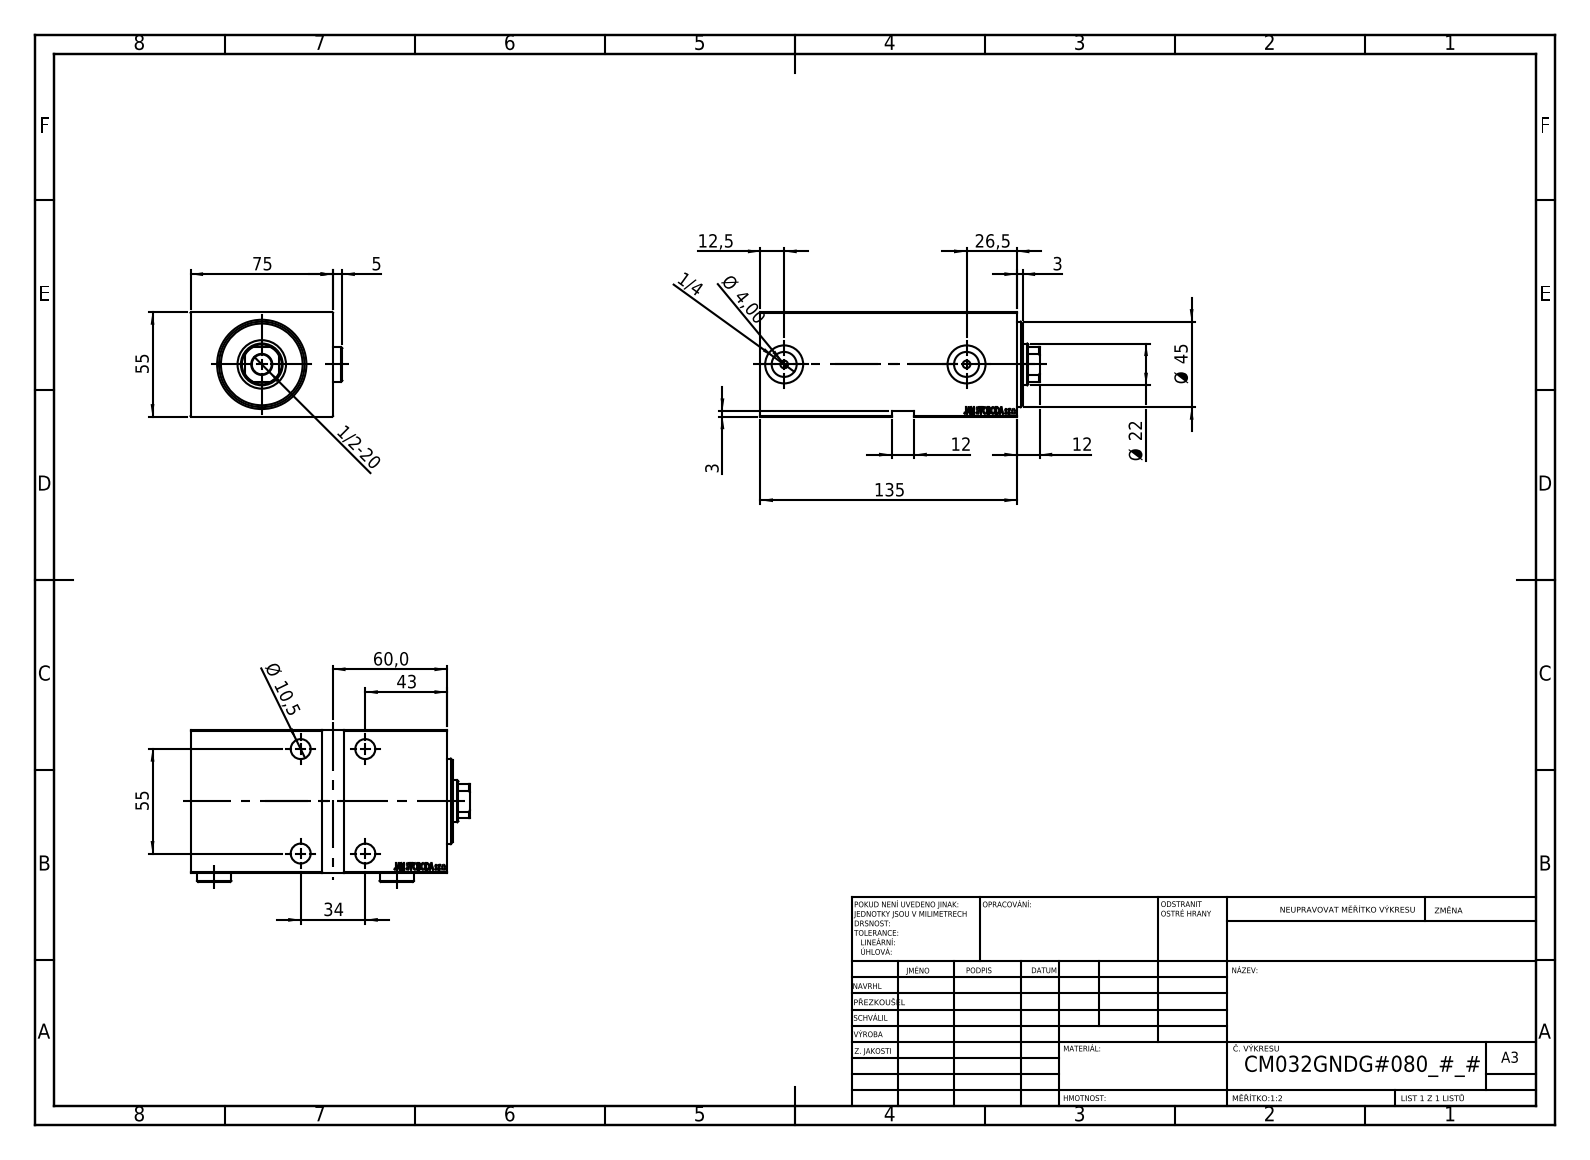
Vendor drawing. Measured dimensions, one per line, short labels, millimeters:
name: Zatka_OIL_PORT; V450CM_G_VCP; V450CM_VC_G; V450CM_G_Body
written by: SolidWorks 2019 (CONFIG_CONTROL_DESIGN)
unit: mm
bodies: 5 solids, 912 faces (446 planar, 68 cylindrical, 398 other)
size: 147 × 79.9 × 55
volume: 491 329 mm³; area: 86 215 mm²
holes: 5× ⌀10.5, 4× ⌀16.5, 2× ⌀4, 2× ⌀13.16, 2× ⌀20, 1× ⌀22, 1× ⌀25.5, 1× ⌀32, 1× ⌀34, 1× ⌀45
bosses: 2× ⌀18, 1× ⌀27
rounds: 1× R10.5
face distances: 55, 75, 135, 5, 3, 130, 10, 120, 125, 74.9
hole spacings: 34, 55, 64.66, 96
